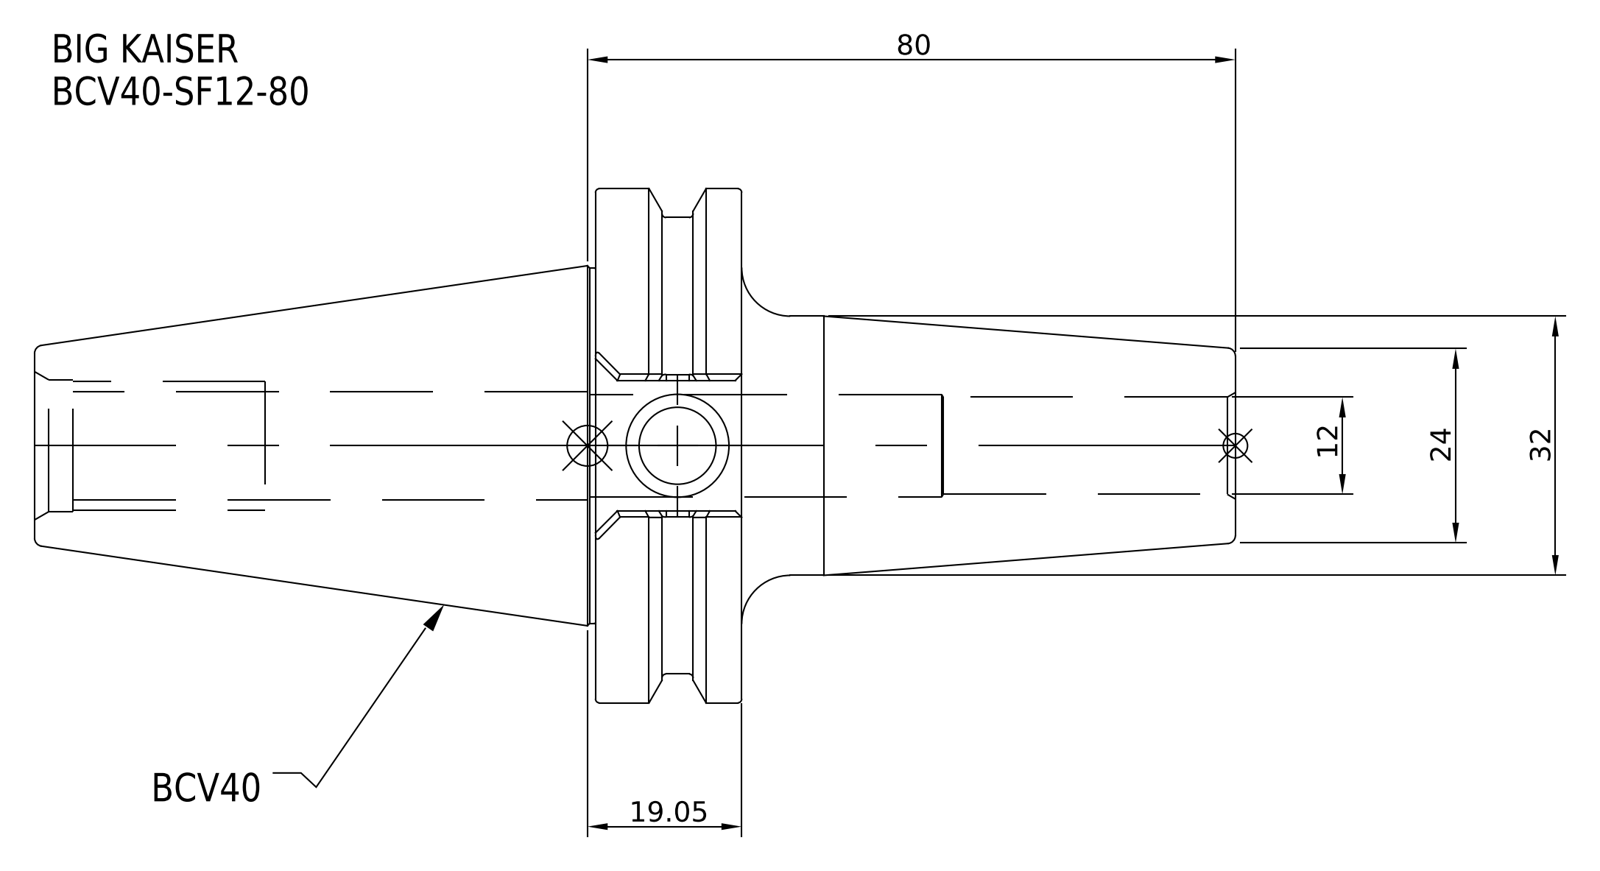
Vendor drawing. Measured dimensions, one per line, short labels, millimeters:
name: BCV40-SF12-80
written by: SolidWorks 2021 (CONFIG_CONTROL_DESIGN)
unit: mm
bodies: 1 solid, 27 faces (7 planar, 12 cylindrical, 8 other)
size: 148.25 × 63.5 × 63.5
volume: 156 408 mm³; area: 23 761 mm²
holes: 1× ⌀12
bosses: 1× ⌀63.5, 1× ⌀56.36, 1× ⌀44.45, 1× ⌀32
face distances: 18.05, 87.3, 69.25, 60.95, 79, 148.25, 66.95, 6, 12.05, 81.3
